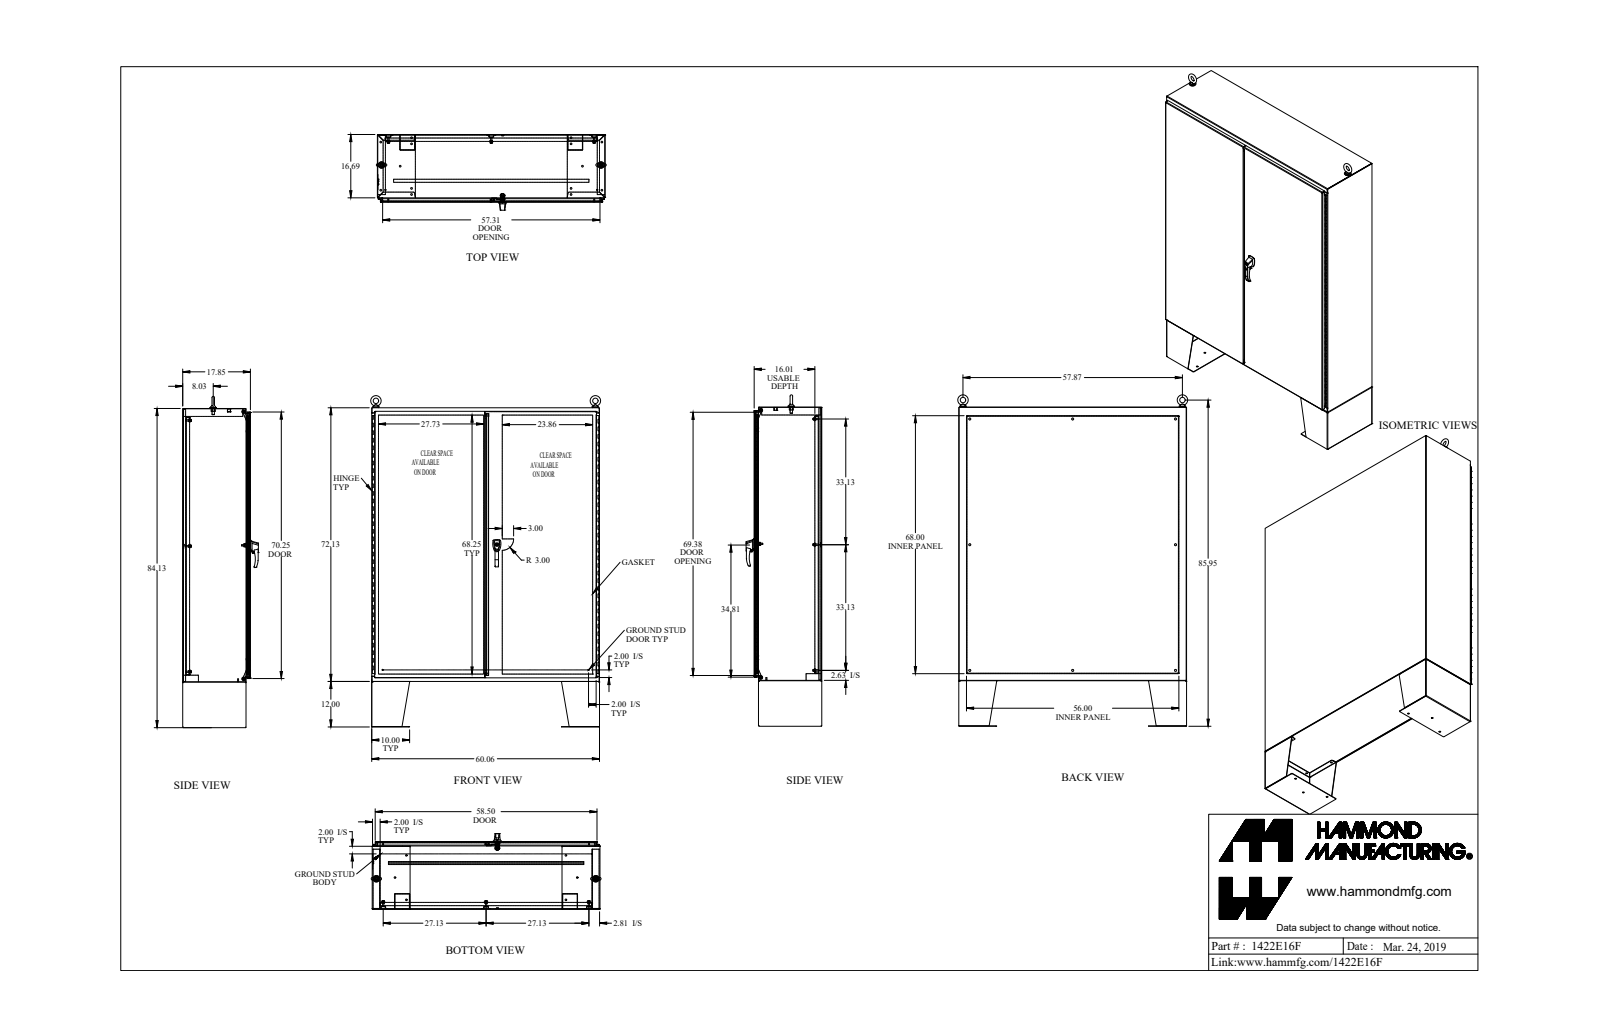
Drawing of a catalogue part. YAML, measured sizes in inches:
part_name: "1422E16F_Default"
step_written_by: "SolidWorks 2019 (CONFIG_CONTROL_DESIGN)"
units: inches
bodies: {solids: 92, faces: 2997, planar: 1372, cylindrical: 1378, other: 247}
overall_size: [87.778, 61.121, 19.963]
volume: 2234
surface_area: 41883
round_holes:
  - {diameter: 0.304, count: 24}
  - {diameter: 0.437, count: 14}
  - {diameter: 0.307, count: 9}
  - {diameter: 0.563, count: 8}
  - {diameter: 0.445, count: 6}
  - {diameter: 0.11, count: 2}
  - {diameter: 0.25, count: 2}
  - {diameter: 0.257, count: 2}
  - {diameter: 0.28, count: 2}
  - {diameter: 0.281, count: 2}
  - {diameter: 0.313, count: 2}
  - {diameter: 0.39, count: 2}
round_bosses_or_shafts:
  - {diameter: 1, count: 10}
  - {diameter: 0.65, count: 8}
  - {diameter: 0.375, count: 8}
  - {diameter: 0.33, count: 8}
  - {diameter: 0.281, count: 6}
  - {diameter: 0.25, count: 4}
  - {diameter: 1.75, count: 2}
  - {diameter: 1.5, count: 2}
partial_cylinders:
  - {radius: 0.048, count: 32}
  - {radius: 0.143, count: 32}
  - {radius: 0.125, count: 22}
  - {radius: 0.018, count: 16}
  - {radius: 0.06, count: 14}
  - {radius: 0.116, count: 12}
  - {radius: 0.187, count: 9}
  - {radius: 0.05, count: 8}
face_to_face_distances: [0.095, 0.125, 17.753, 17.628, 17.723, 17.848, 0.125, 1.687, 16.036, 15.941]
hole_center_spacings: [6, 12, 58.7, 59.613, 18, 61.104, 24, 63.132]
